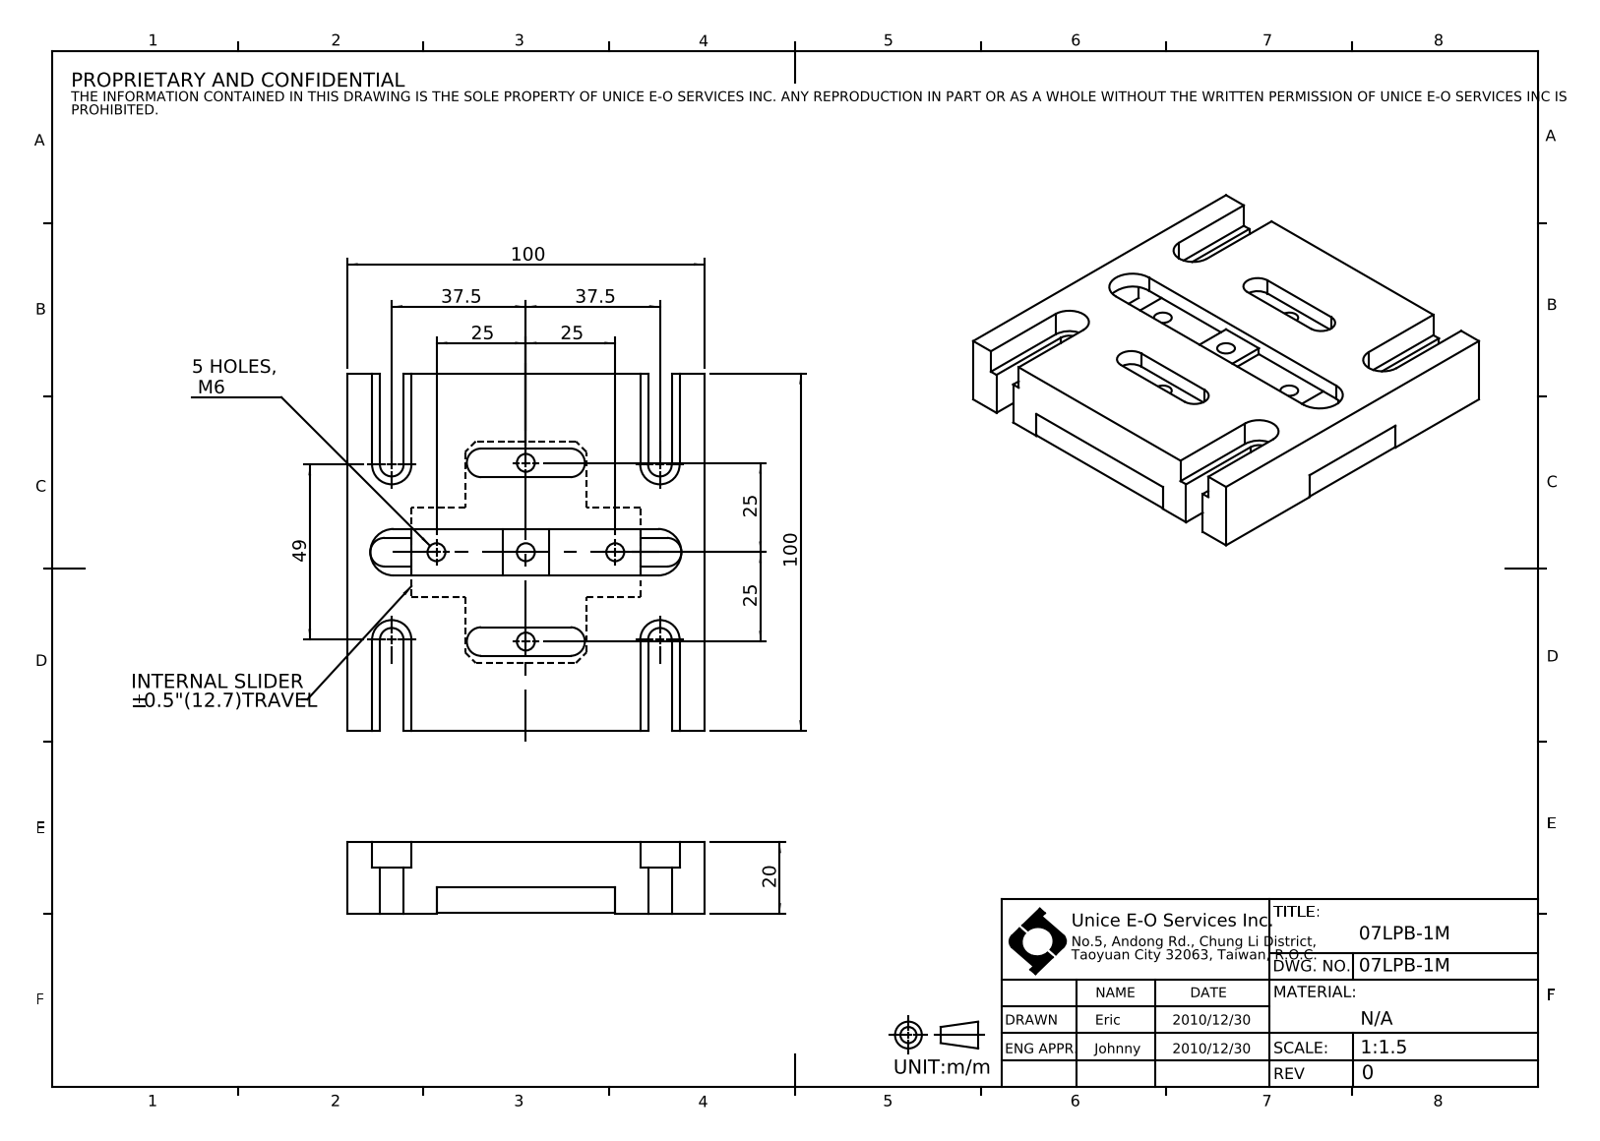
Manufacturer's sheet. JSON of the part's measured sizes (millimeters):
{"part_name": "07LPB-1M", "step_written_by": "SolidWorks 2016 (CONFIG_CONTROL_DESIGN)", "units": "millimeters", "bodies": {"solids": 3, "faces": 179, "planar": 103, "cylindrical": 68, "other": 8}, "overall_size": [100, 100, 20], "volume_mm3": 147420, "surface_area_mm2": 57844, "round_holes": [[5, 5], [3.3, 4], [4.5, 4], [8, 4]], "partial_cylinders_radius": [[3.5, 8], [4, 6], [3.3, 4], [5.5, 4], [6.5, 2]], "face_to_face_distances": [8, 12.5, 4.5, 7.3, 15.3, 19.8, 75, 25, 100, 33], "hole_center_spacings": [43.34, 25, 20.7, 35.36, 55.93, 67.66, 50, 83]}
